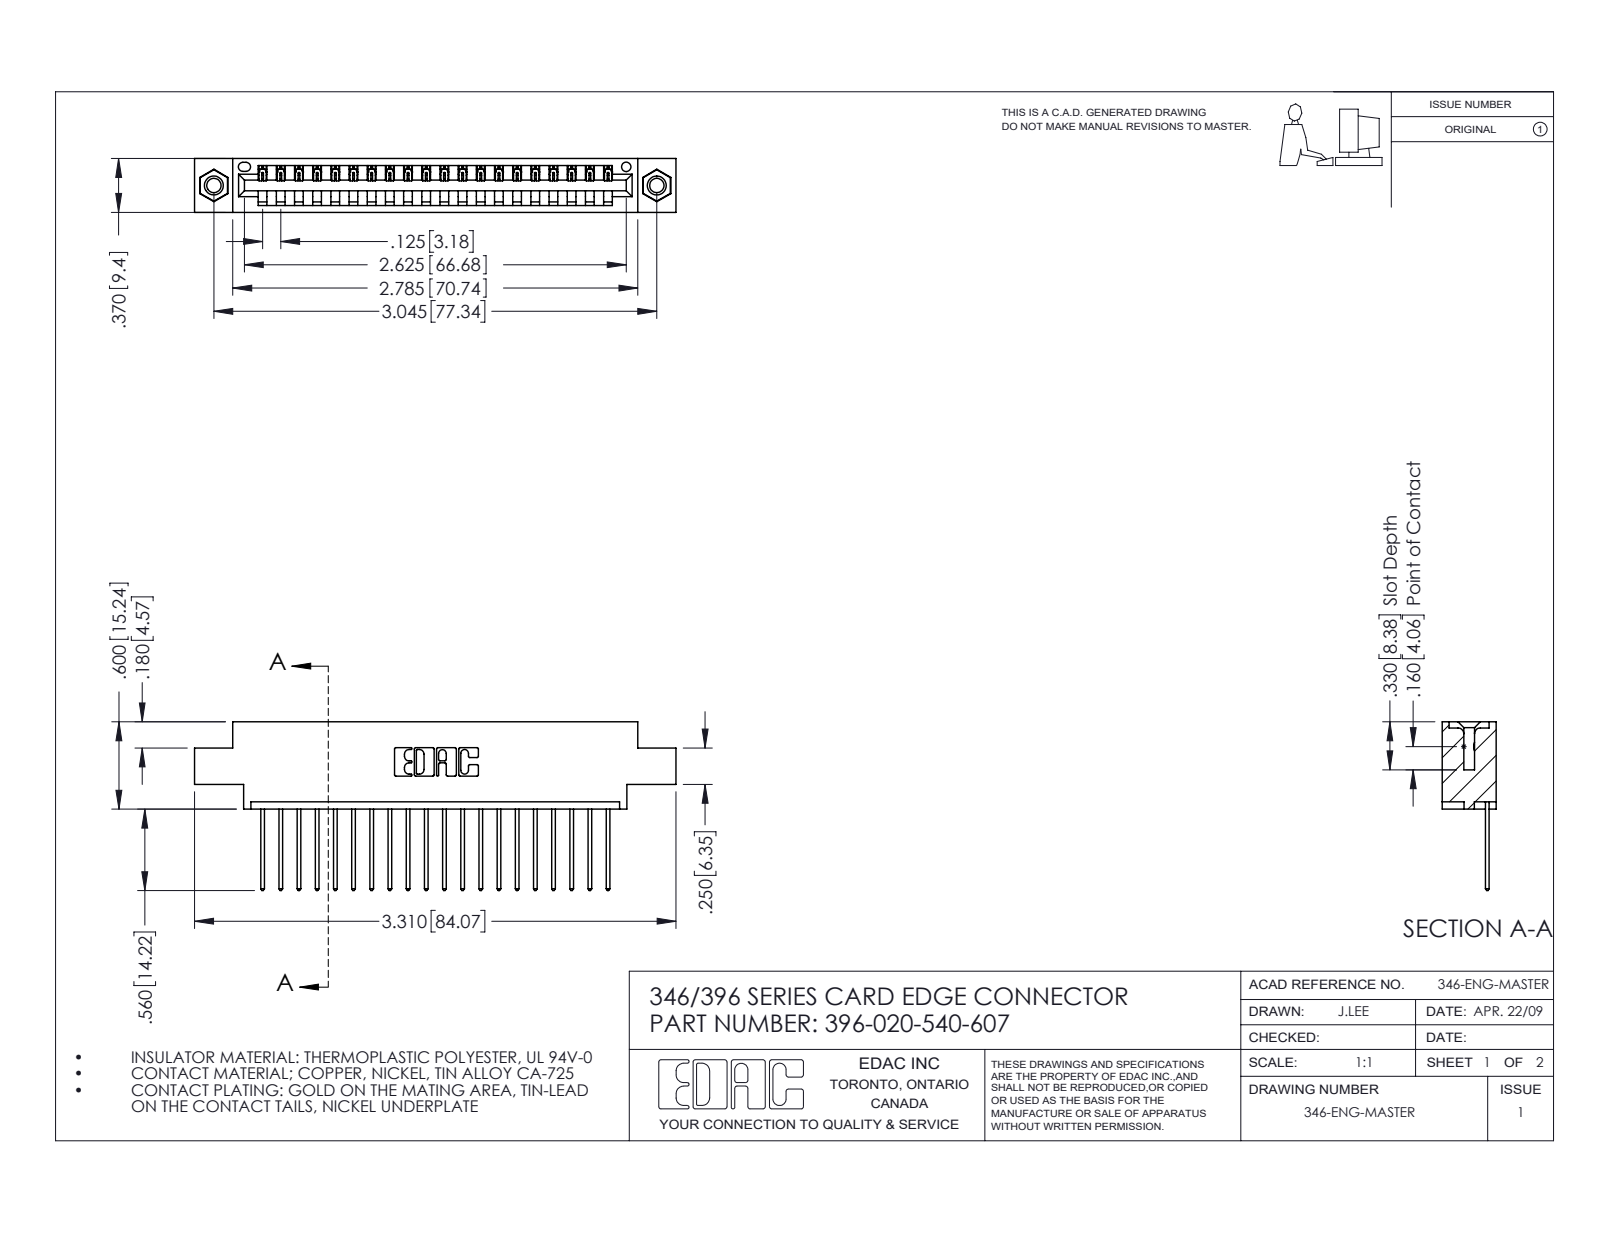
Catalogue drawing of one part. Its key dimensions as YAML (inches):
part_name: "345-292-001_345-293-140; 345-250-001_345-250-005-103; 396-020-540-607; 346 Part_0.170 Offset - 0.156 Dia-TI"
step_written_by: "SolidWorks 2016 (CONFIG_CONTROL_DESIGN)"
units: inches
bodies: {solids: 23, faces: 1346, planar: 912, cylindrical: 418, other: 16}
overall_size: [3.31, 1.16, 0.37]
volume: 0.473
surface_area: 15.26
round_holes:
  - {diameter: 0.098, count: 2}
  - {diameter: 0.125, count: 2}
  - {diameter: 0.156, count: 2}
  - {diameter: 0.064, count: 1}
round_bosses_or_shafts:
  - {diameter: 0.155, count: 2}
partial_cylinders:
  - {radius: 0.006, count: 40}
  - {radius: 0.01, count: 40}
  - {radius: 0.01, count: 22}
  - {radius: 0.007, count: 6}
  - {radius: 0.031, count: 6}
  - {radius: 0.026, count: 3}
  - {radius: 0.031, count: 2}
  - {radius: 0.04, count: 2}
face_to_face_distances: [0.048, 0.322, 0.37, 0.25, 0.072, 0.298, 0.025, 0.222, 0.148, 0.1]
hole_center_spacings: [0.246, 2.837, 3.045]
